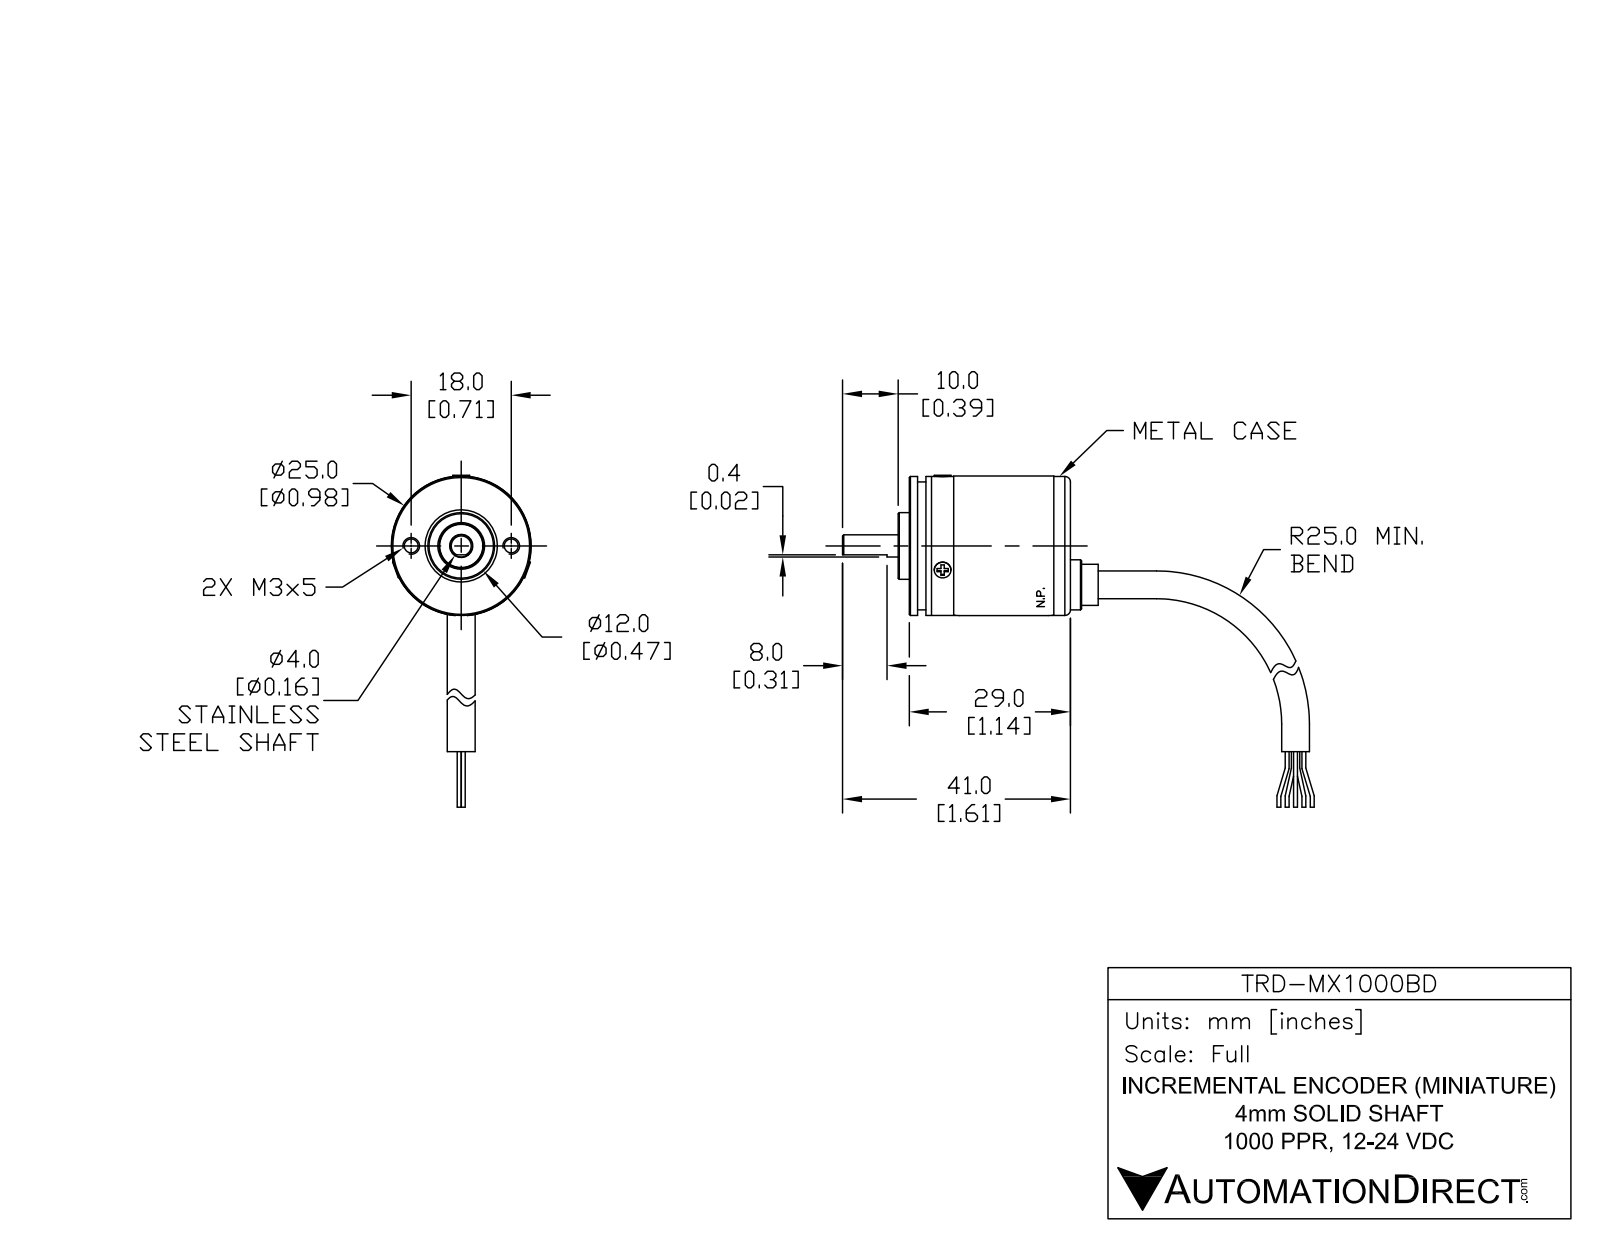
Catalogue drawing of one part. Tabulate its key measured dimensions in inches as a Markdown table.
| quantity | value |
| --- | --- |
| part name | TRD-MX_SW0002_1_ASM; TRD-MX_D; MANIFOLD_SOLID_BREP_5744 |
| STEP written by | SolidWorks 2016 (AUTOMOTIVE_DESIGN) |
| units | inches |
| bodies | 1 solid, 161 faces (62 planar, 71 cylindrical, 28 other) |
| overall size | 3.341 × 2.35 × 0.984 |
| volume | 0.961 in³ |
| surface area | 7.443 in² |
| round holes (diameter × count) | 0.098 × 2, 0.11 × 2, 0.315 × 1 |
| round bosses / shafts (diameter × count) | 0.028 × 13, 0.118 × 3, 0.197 × 2, 0.079 × 2, 0.984 × 1, 0.906 × 1, 0.472 × 1, 0.354 × 1 |
| partial cylindrical surfaces (radius × count) | 0.472 × 1 |
| main face-to-face distances | 1.142, 0.059, 1.22, 0.079, 0.118, 0.197, 1.024, 0.138, 1.083, 1.394 |
| hole center spacings | 0.354, 0.709 |
